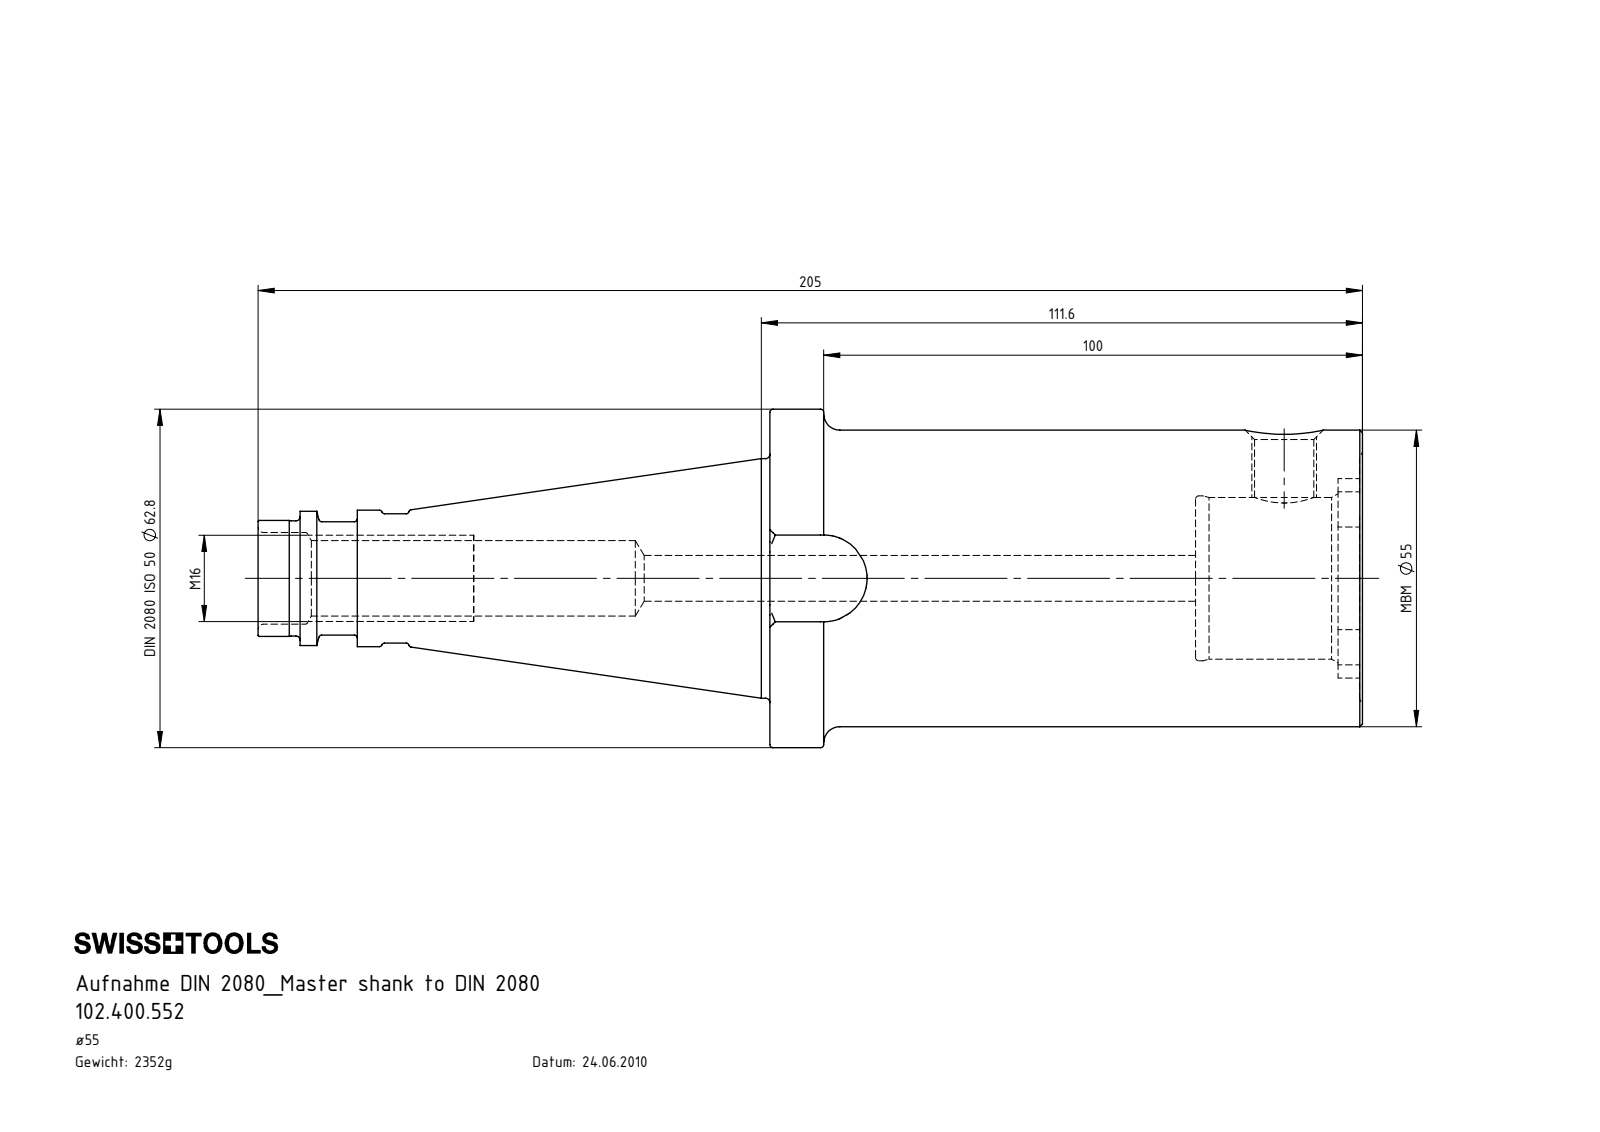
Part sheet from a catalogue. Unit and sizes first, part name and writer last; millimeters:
Units: millimetres
Overall size (bounding box): 205 × 62.8 × 60.7
Round holes (diameter × count): ⌀8.5 ×1, ⌀11 ×1, ⌀14 ×1, ⌀17 ×1, ⌀30 ×1, ⌀30.6 ×1
Round bosses / shafts (diameter × count): ⌀62.8 ×1, ⌀55 ×1, ⌀44.45 ×1, ⌀25.3 ×1, ⌀24.91 ×1, ⌀24 ×1, ⌀21.5 ×1, ⌀21.35 ×1
Partial cylindrical surfaces — rounded edges, fillets, slot ends (radius × count): R1.6 ×8, R5.2 ×4, R8.05 ×1, R18.5 ×1, R21.27 ×1
Main face-to-face distances: 79, 110, 31, 105.45, 26.45, 4.55, 109.45, 30.45, 4, 0.55
Volume: 299 682 mm³ · Surface area: 42 826 mm²
Bodies: 1 solid, 137 faces (30 planar, 52 cylindrical, 55 other)
Part name (STEP PRODUCT): 102.400.552
STEP written by: SolidWorks 2017 (CONFIG_CONTROL_DESIGN)
